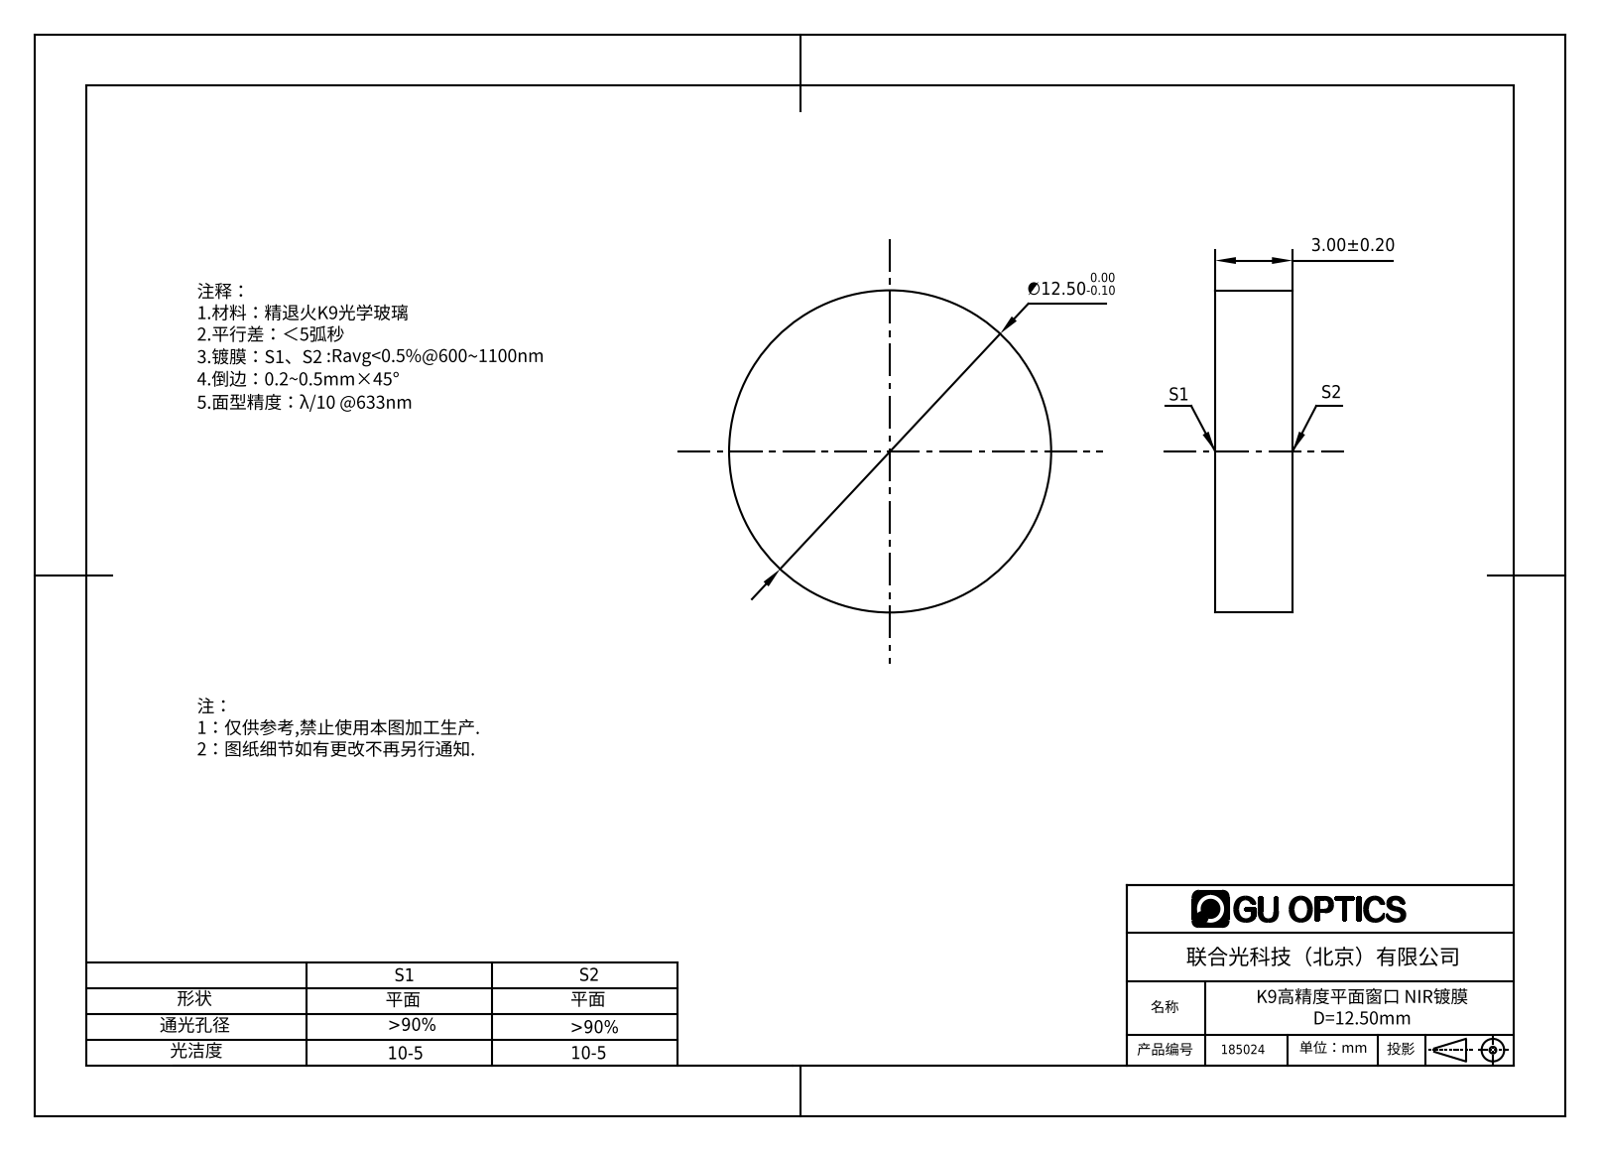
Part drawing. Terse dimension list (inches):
name: 185002
written by: SolidWorks 2016 (AUTOMOTIVE_DESIGN)
unit: in
bodies: 1 solid, 4 faces (2 planar, 2 cylindrical, 0 other)
size: 0.492 × 0.492 × 0.118
volume: 0.022 in³; area: 0.563 in²
bosses: 1× ⌀0.492
face distances: 0.118
